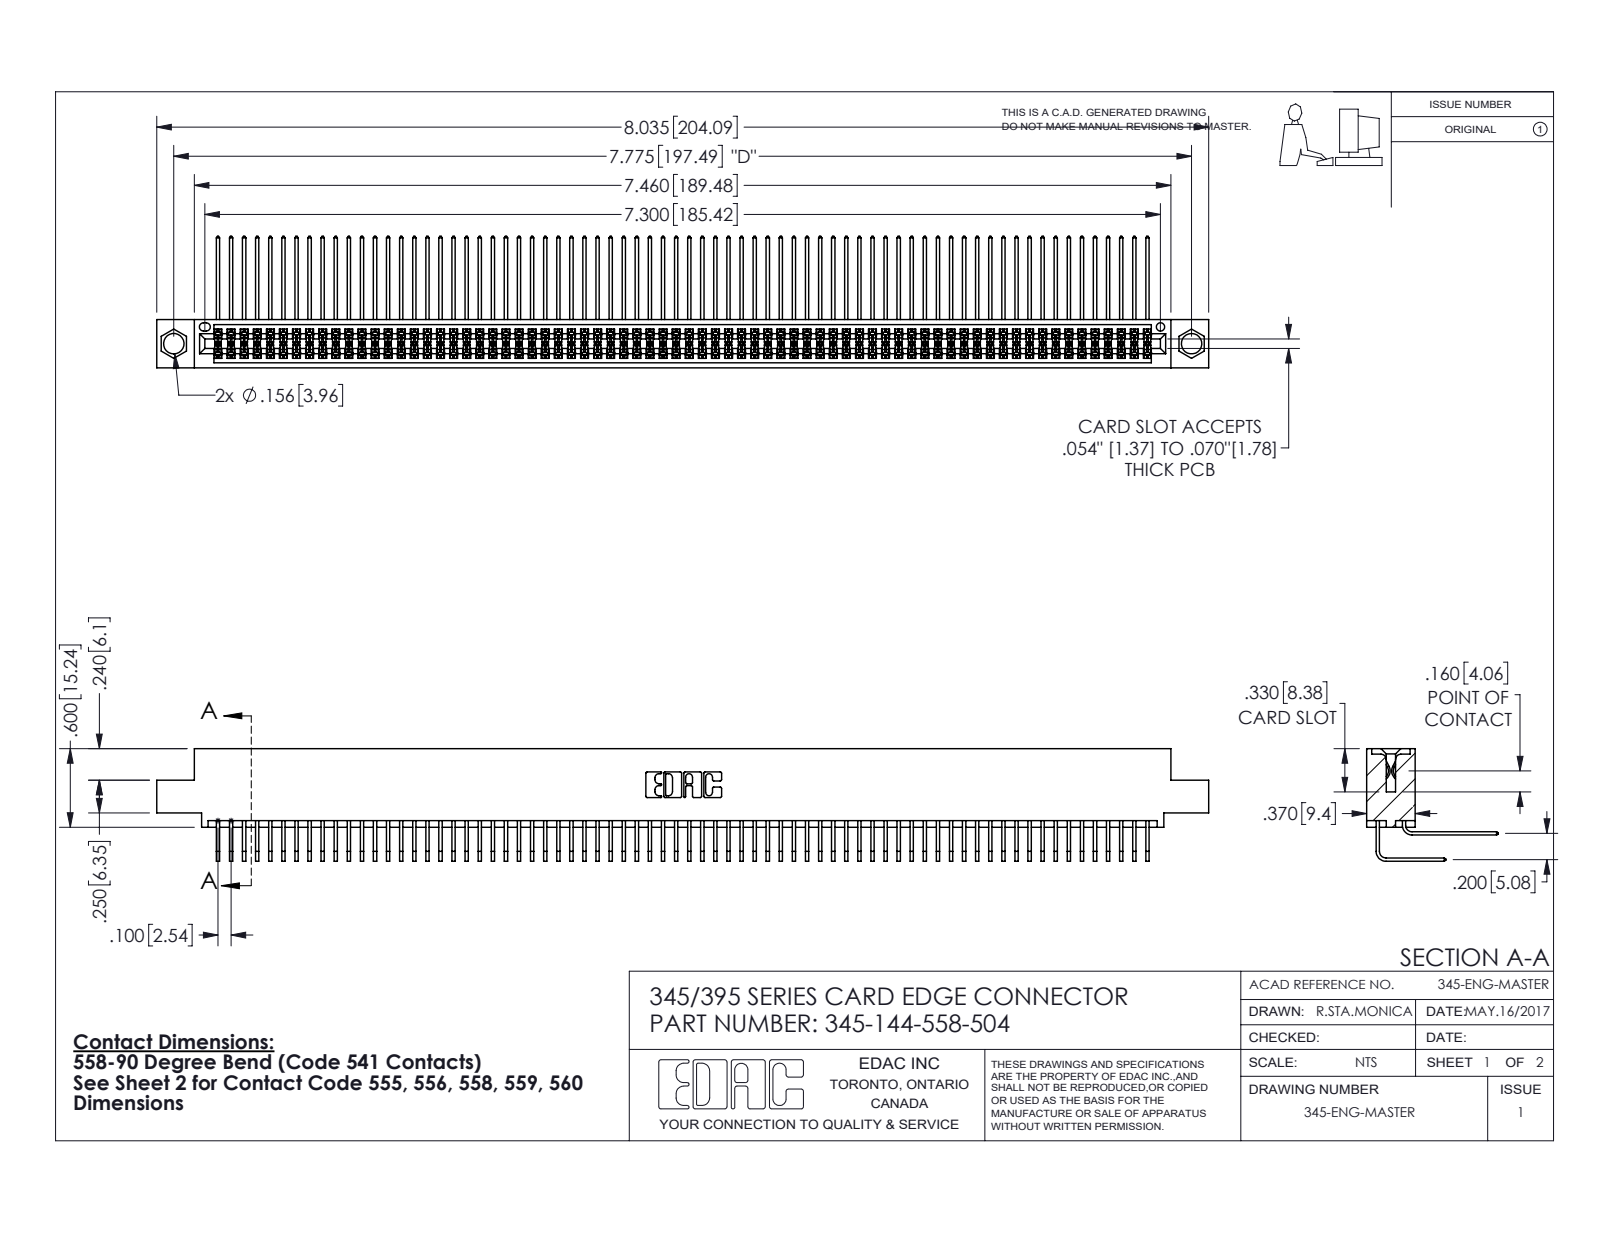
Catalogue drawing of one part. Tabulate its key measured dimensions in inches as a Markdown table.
| quantity | value |
| --- | --- |
| part name | 345-292-001_558 Tail - 2; 345-144-558-504; 345 Part_0.110 Offset - 0.156 Dia-TI; 345-292-001_558 559 Tail - 1 |
| STEP written by | SolidWorks 2020 (CONFIG_CONTROL_DESIGN) |
| units | inches |
| bodies | 145 solids, 7632 faces (5138 planar, 2494 cylindrical, 0 other) |
| overall size | 8.035 × 1.005 × 0.859 |
| volume | 1.267 in³ |
| surface area | 54.42 in² |
| round holes (diameter × count) | 0.156 × 2, 0.064 × 1 |
| partial cylindrical surfaces (radius × count) | 0.006 × 288, 0.01 × 22, 0.007 × 6, 0.031 × 6, 0.026 × 3, 0.014 × 2, 0.019 × 2, 0.022 × 2 |
| main face-to-face distances | 0.072, 0.298, 0.2, 0.37, 0.098, 0.272, 0.025, 0.225, 0.025, 0.175 |
| hole center spacings | 0.27, 7.539, 7.775 |
